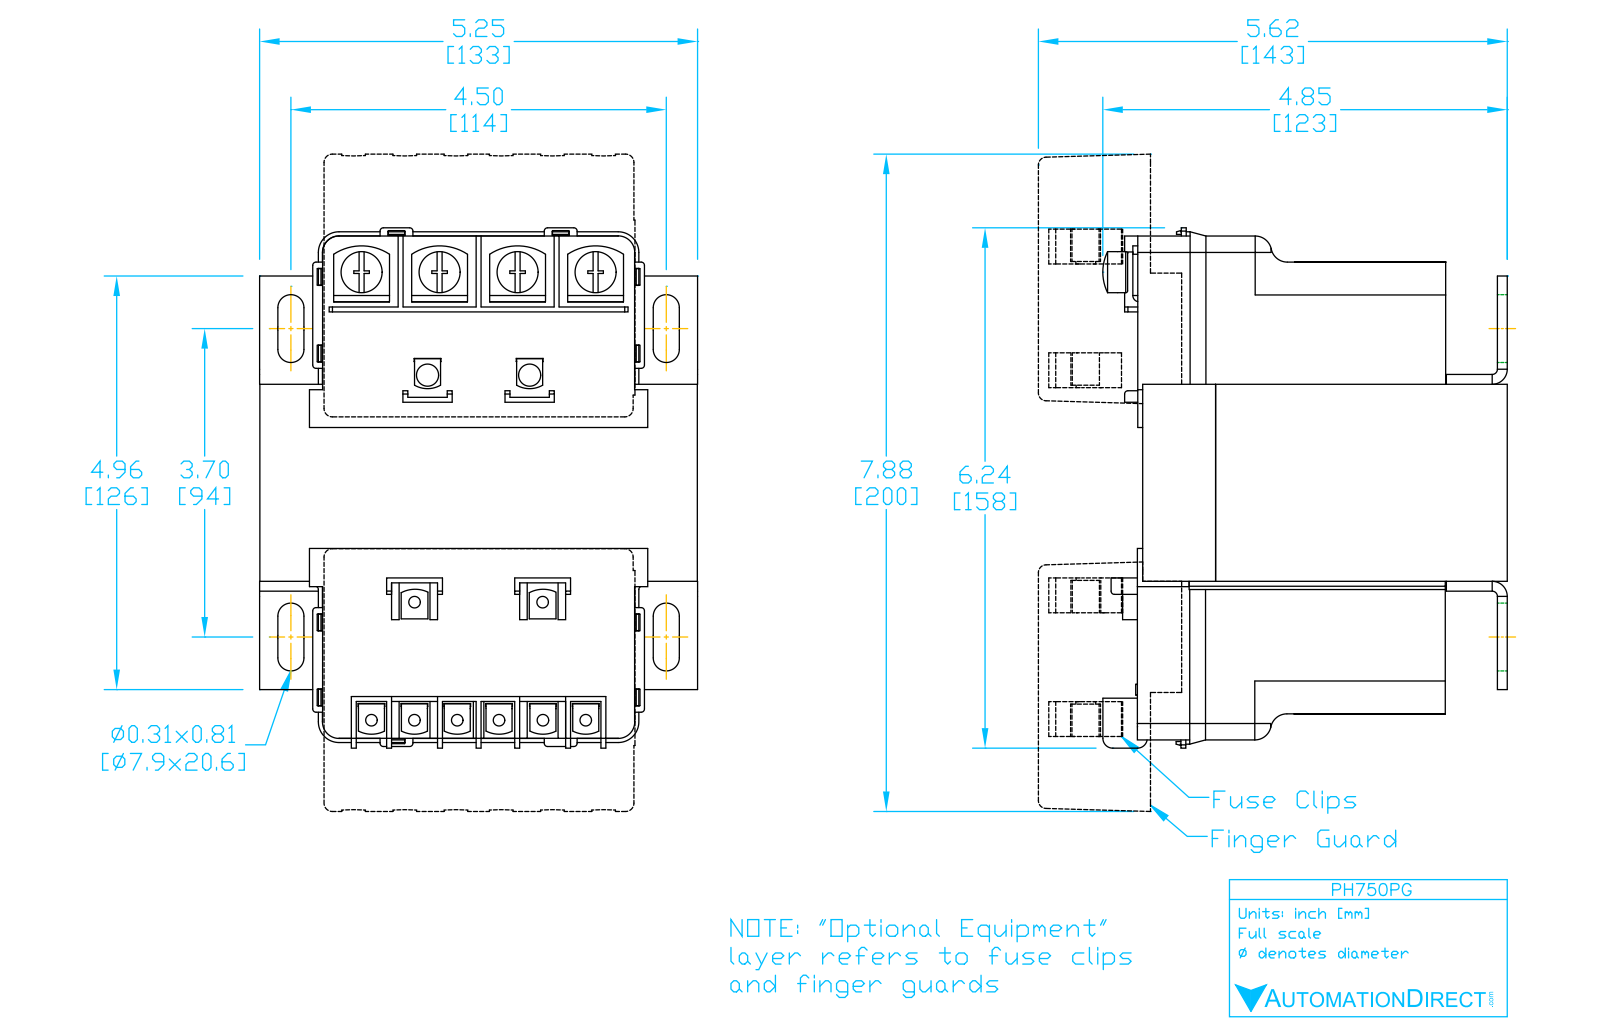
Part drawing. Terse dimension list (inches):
name: PH750PG
written by: SolidWorks 2017 (AUTOMOTIVE_DESIGN)
unit: in
bodies: 7 solids, 680 faces (390 planar, 206 cylindrical, 84 other)
size: 5.979 × 5.25 × 4.847
volume: 103.1 in³; area: 290 in²
holes: 2× ⌀0.157, 2× ⌀0.315
rounds: 98× R0.039, 10× R0.197, 4× R0.1, 4× R0.156, 4× R0.248, 4× R0.394, 2× R0.157, 1× R0.062
face distances: 2.362, 0.318, 0.752, 4.492, 3.496, 3.814, 4.37, 0.874, 0.556, 4.847
hole spacings: 3.543, 4.37
